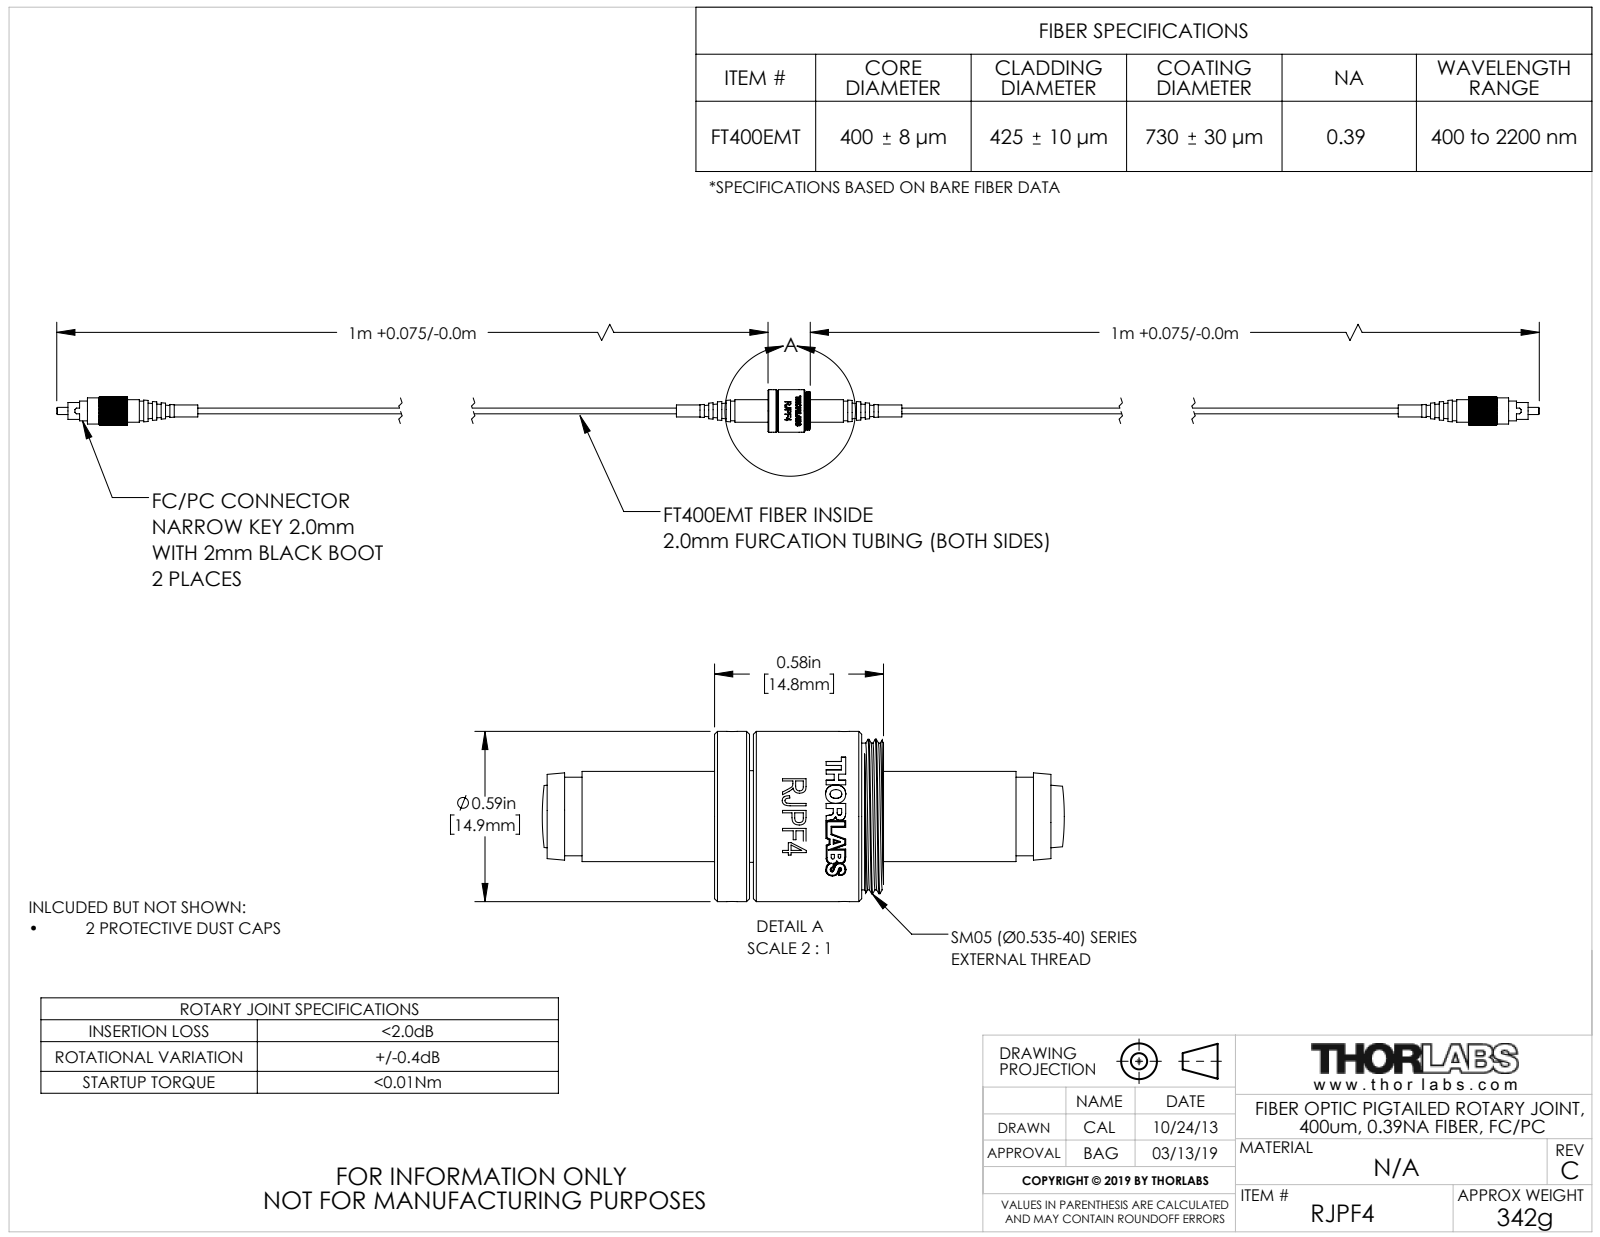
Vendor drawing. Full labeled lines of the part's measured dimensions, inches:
Part name (STEP PRODUCT): TTN020009-E0W
STEP written by: SolidWorks 2018 (AUTOMOTIVE_DESIGN)
Units: inches
Bodies: 49 solids, 1643 faces (543 planar, 659 cylindrical, 441 other)
Overall size (bounding box): 83.66 × 0.585 × 0.585
Volume: 0.774 in³ · Surface area: 38.18 in²
Round holes (diameter × count): ⌀0.036 ×2, ⌀0.009 ×1, ⌀0.056 ×1, ⌀0.085 ×1, ⌀0.09 ×1, ⌀0.098 ×1, ⌀0.141 ×1, ⌀0.183 ×1, ⌀0.192 ×1, ⌀0.21 ×1, ⌀0.25 ×1, ⌀0.276 ×1
Round bosses / shafts (diameter × count): ⌀0.585 ×1, ⌀0.531 ×1, ⌀0.504 ×1, ⌀0.433 ×1, ⌀0.429 ×1, ⌀0.406 ×1, ⌀0.397 ×1, ⌀0.36 ×1
Partial cylindrical surfaces — rounded edges, fillets, slot ends (radius × count): R0.016 ×36, R0.023 ×18, R0.008 ×8, R0.197 ×1, R0.292 ×1
Main face-to-face distances: 0.267, 0.581, 0.461, 0.12, 0.447, 0.013, 0.133, 0.118, 0.126, 40.859
Hole centre spacings: 0.386
